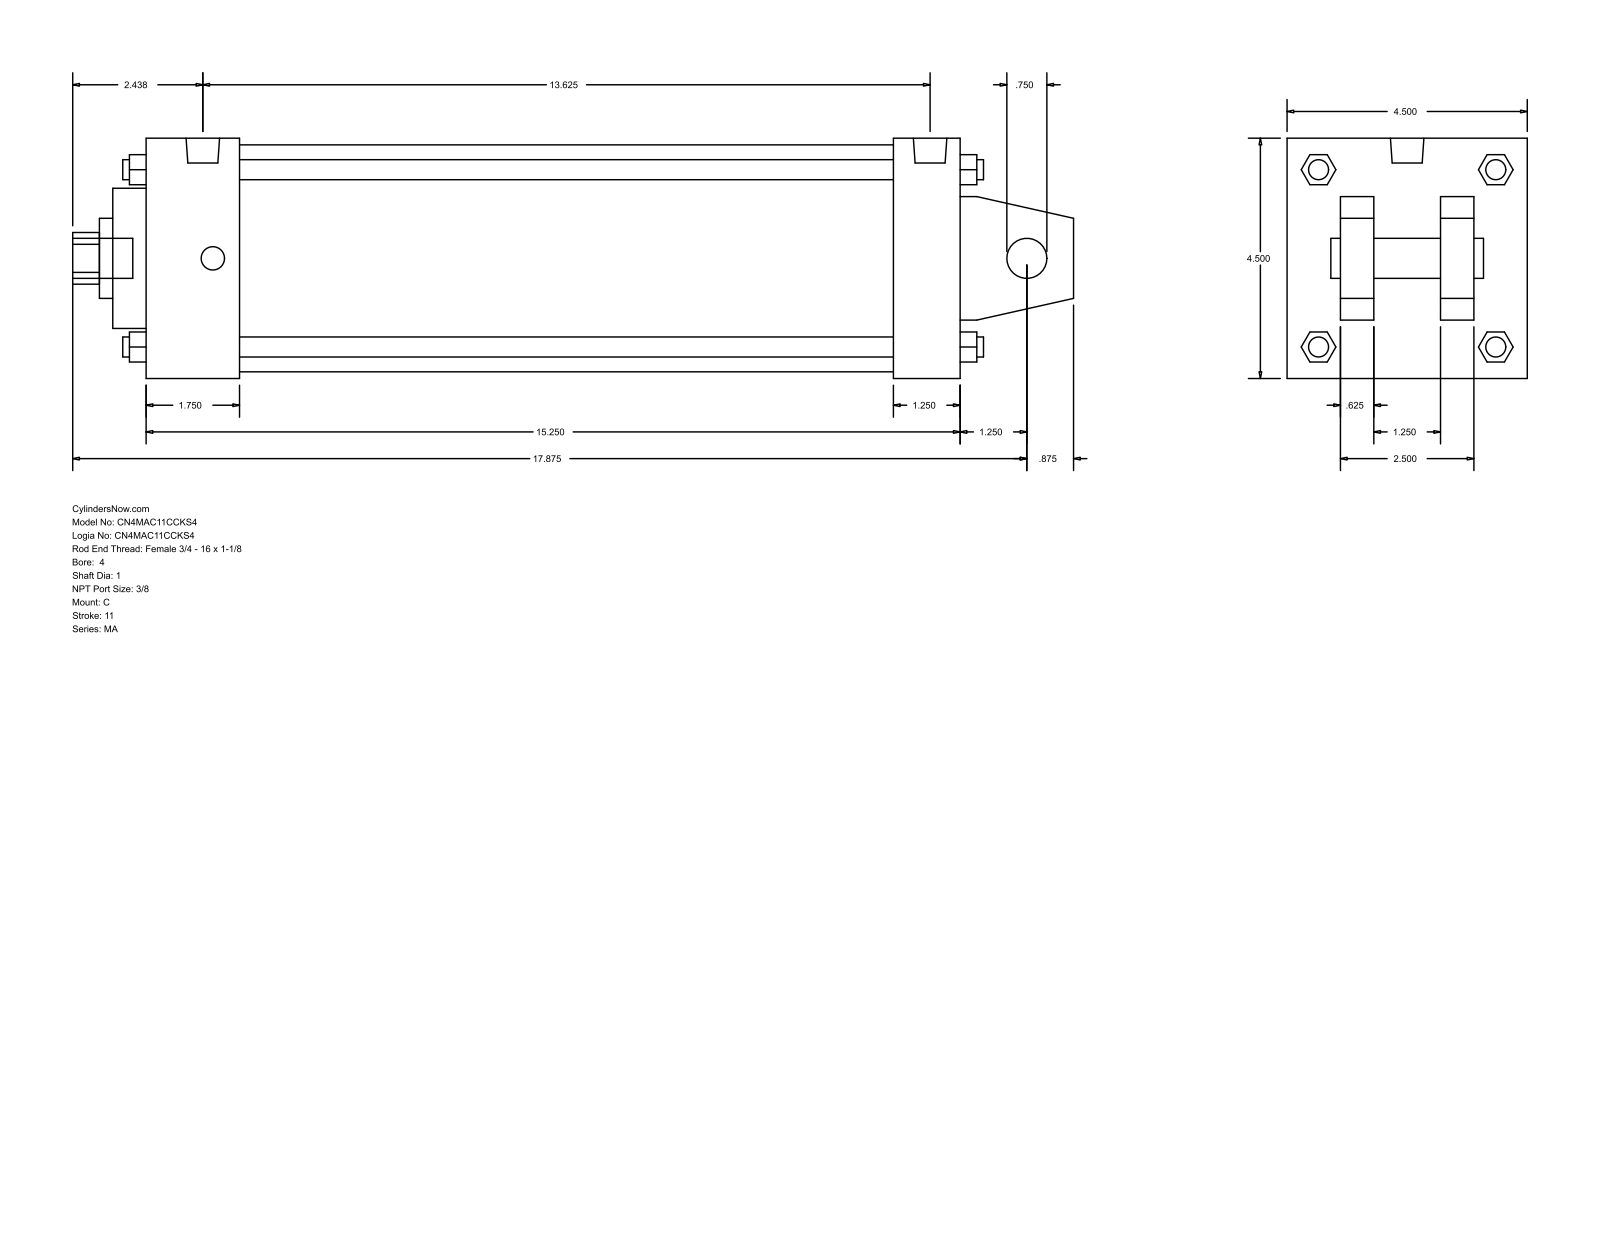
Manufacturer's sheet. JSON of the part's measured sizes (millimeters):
{"part_name": "MA_C__0400_1", "step_written_by": "GSSL Pune (CONFIG_CONTROL_DESIGN)", "units": "millimeters", "bodies": {"solids": 0, "faces": 141, "planar": 109, "cylindrical": 32, "other": 0}, "overall_size": [476.25, 114.3, 114.3], "round_holes": [[19.05, 1], [25.4, 1], [38.1, 1], [66.67, 1], [107.95, 1]], "round_bosses_or_shafts": [[11.11, 4], [9.53, 4], [15.93, 2], [19.05, 1]], "partial_cylinders_radius": [[12.29, 1]], "face_to_face_distances": [114.3, 387.35, 15.87, 73.03, 41.27, 25.4, 88.9, 47.63, 355.6, 31.75]}
